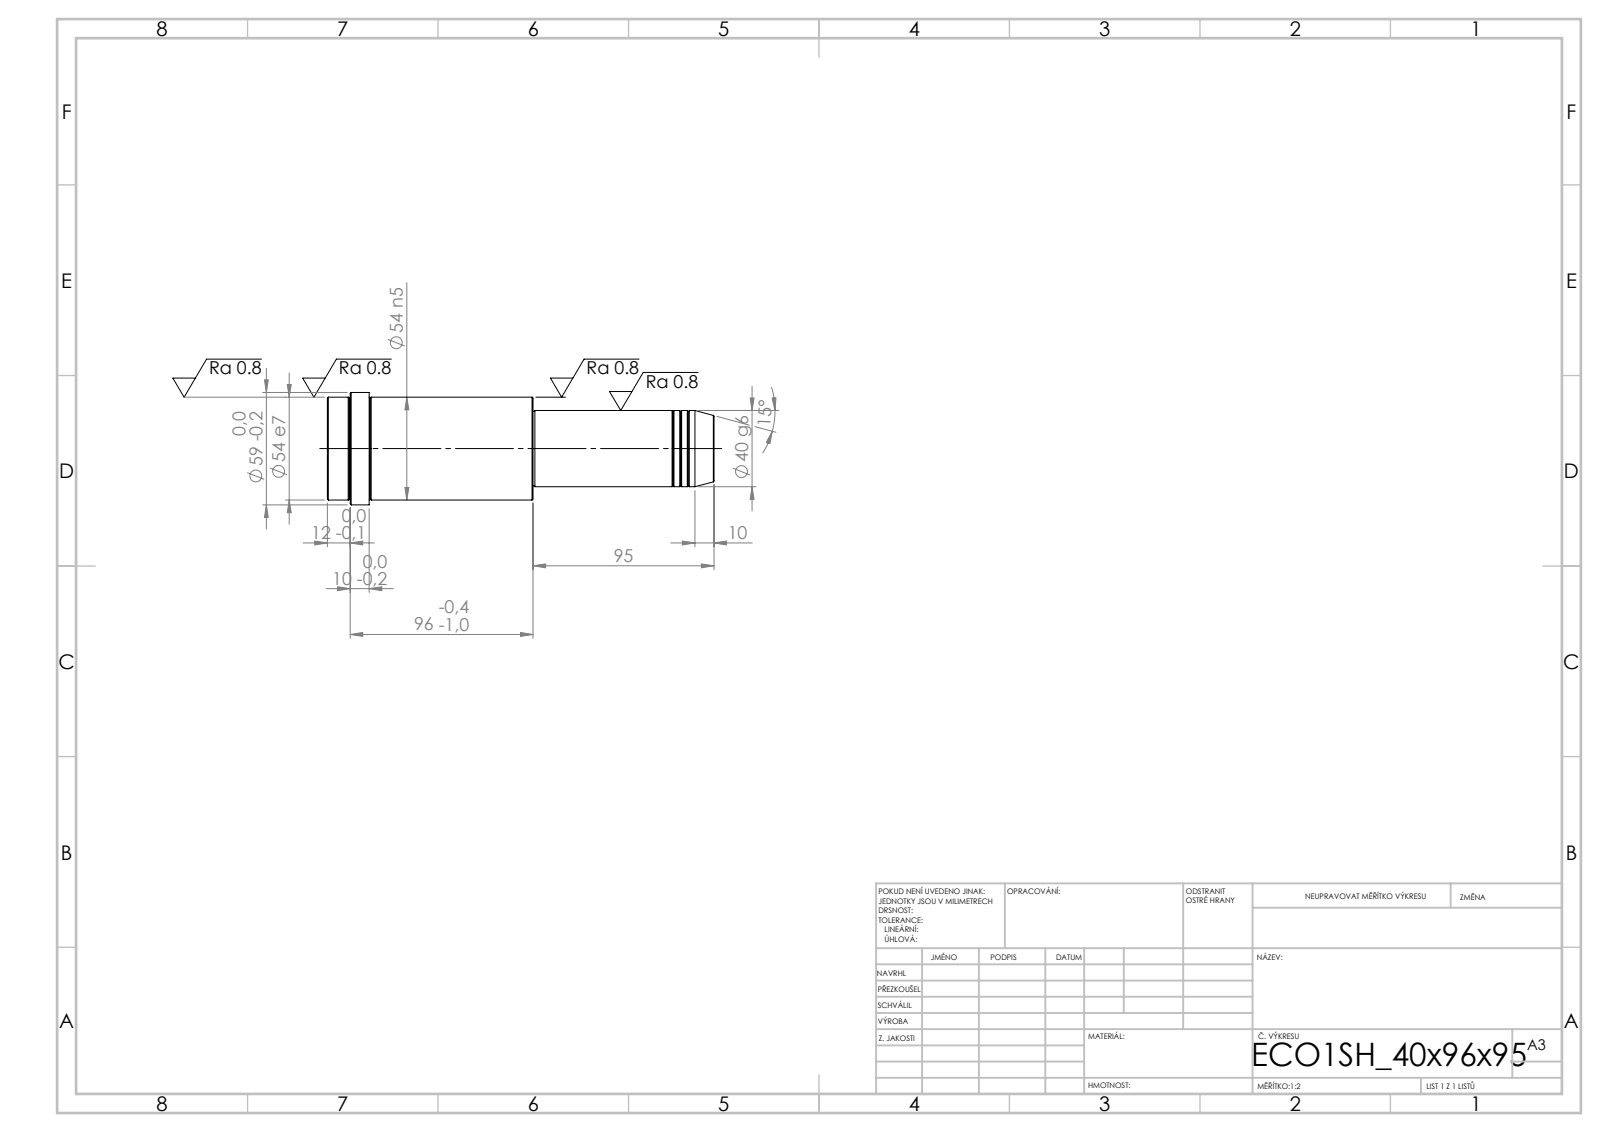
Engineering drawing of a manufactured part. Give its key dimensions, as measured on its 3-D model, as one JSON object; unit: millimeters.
{"step_written_by": "SolidWorks 2019 (CONFIG_CONTROL_DESIGN)", "units": "millimeters", "bodies": {"solids": 1, "faces": 52, "planar": 6, "cylindrical": 16, "other": 30}, "overall_size": [203, 59, 59], "volume_mm3": 369145, "surface_area_mm2": 35875, "round_bosses_or_shafts": [[59, 1], [54, 1], [40, 1], [39, 1]], "face_to_face_distances": [108, 95, 203, 181, 86, 22, 191, 96, 10, 12]}
